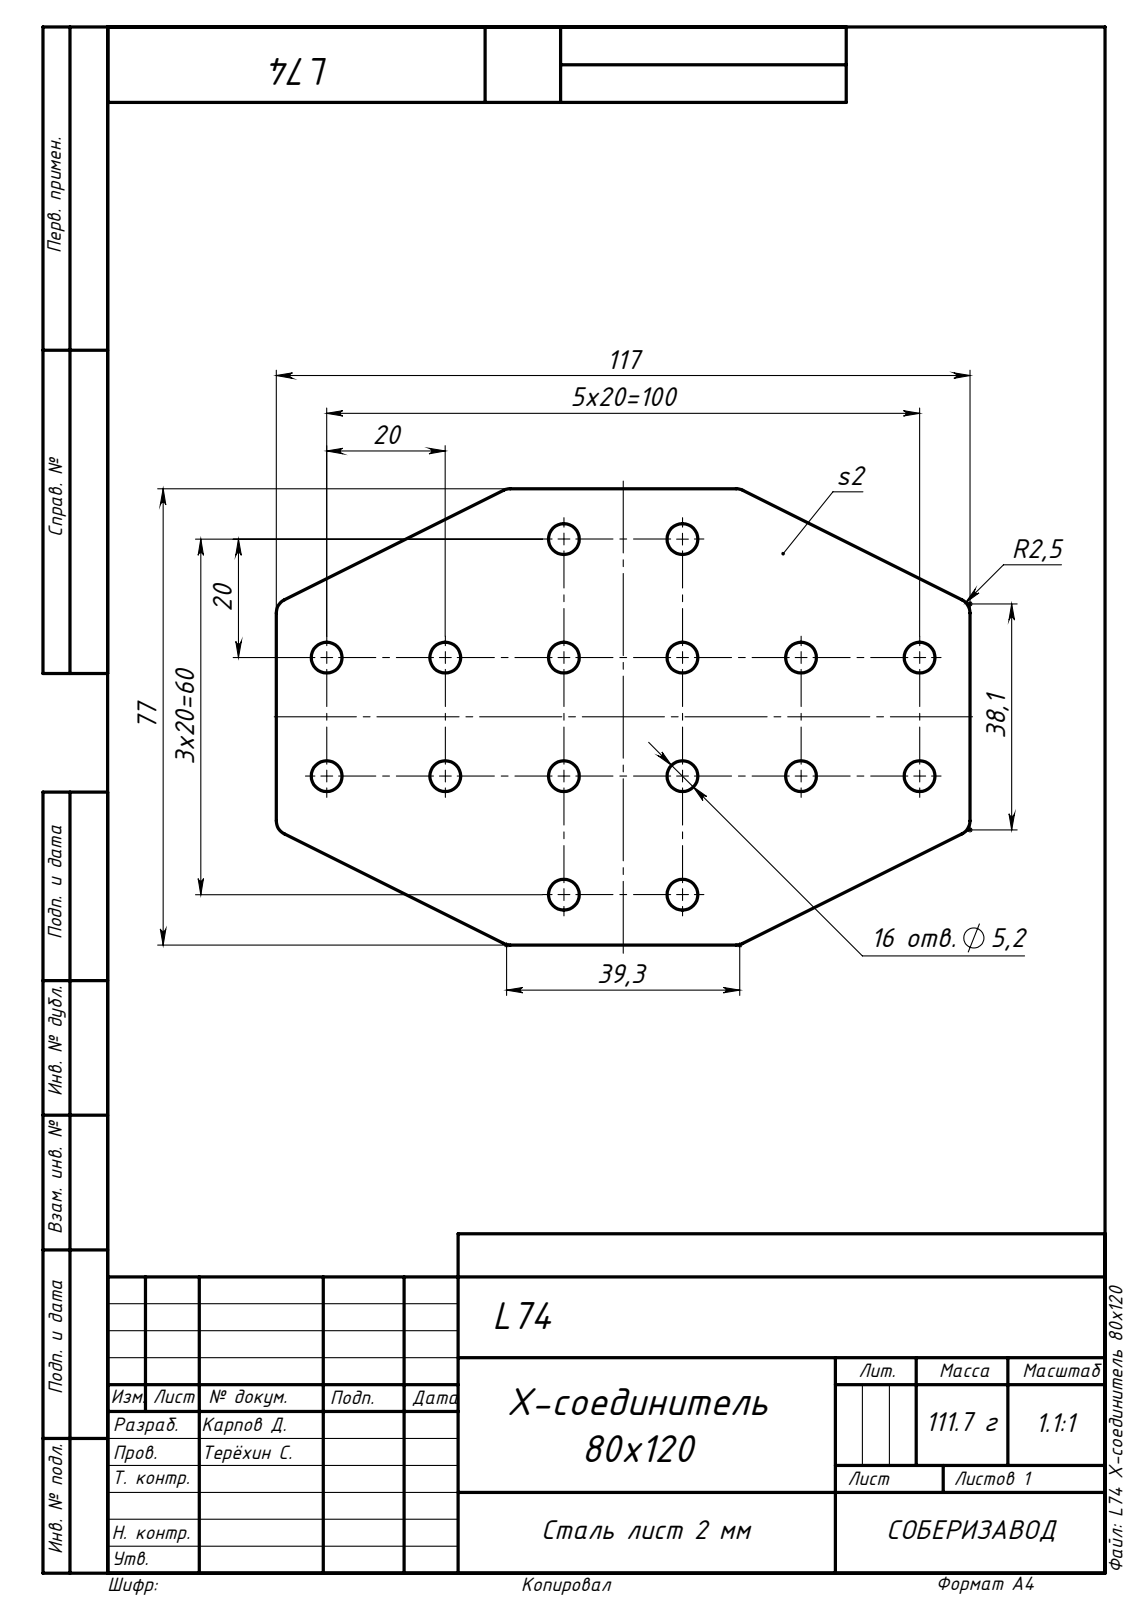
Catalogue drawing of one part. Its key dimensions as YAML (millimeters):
step_written_by: "SolidWorks 2019 (AUTOMOTIVE_DESIGN)"
units: millimeters
bodies: {solids: 1, faces: 50, planar: 10, cylindrical: 40, other: 0}
overall_size: [117, 77, 2]
volume: 14316
surface_area: 15493
round_holes:
  - {diameter: 5.2, count: 16}
partial_cylinders:
  - {radius: 2.5, count: 8}
face_to_face_distances: [2, 86.4, 77, 117]
hole_center_spacings: [44.72, 20, 28.28, 40, 63.25, 56.57, 60, 72.11]
